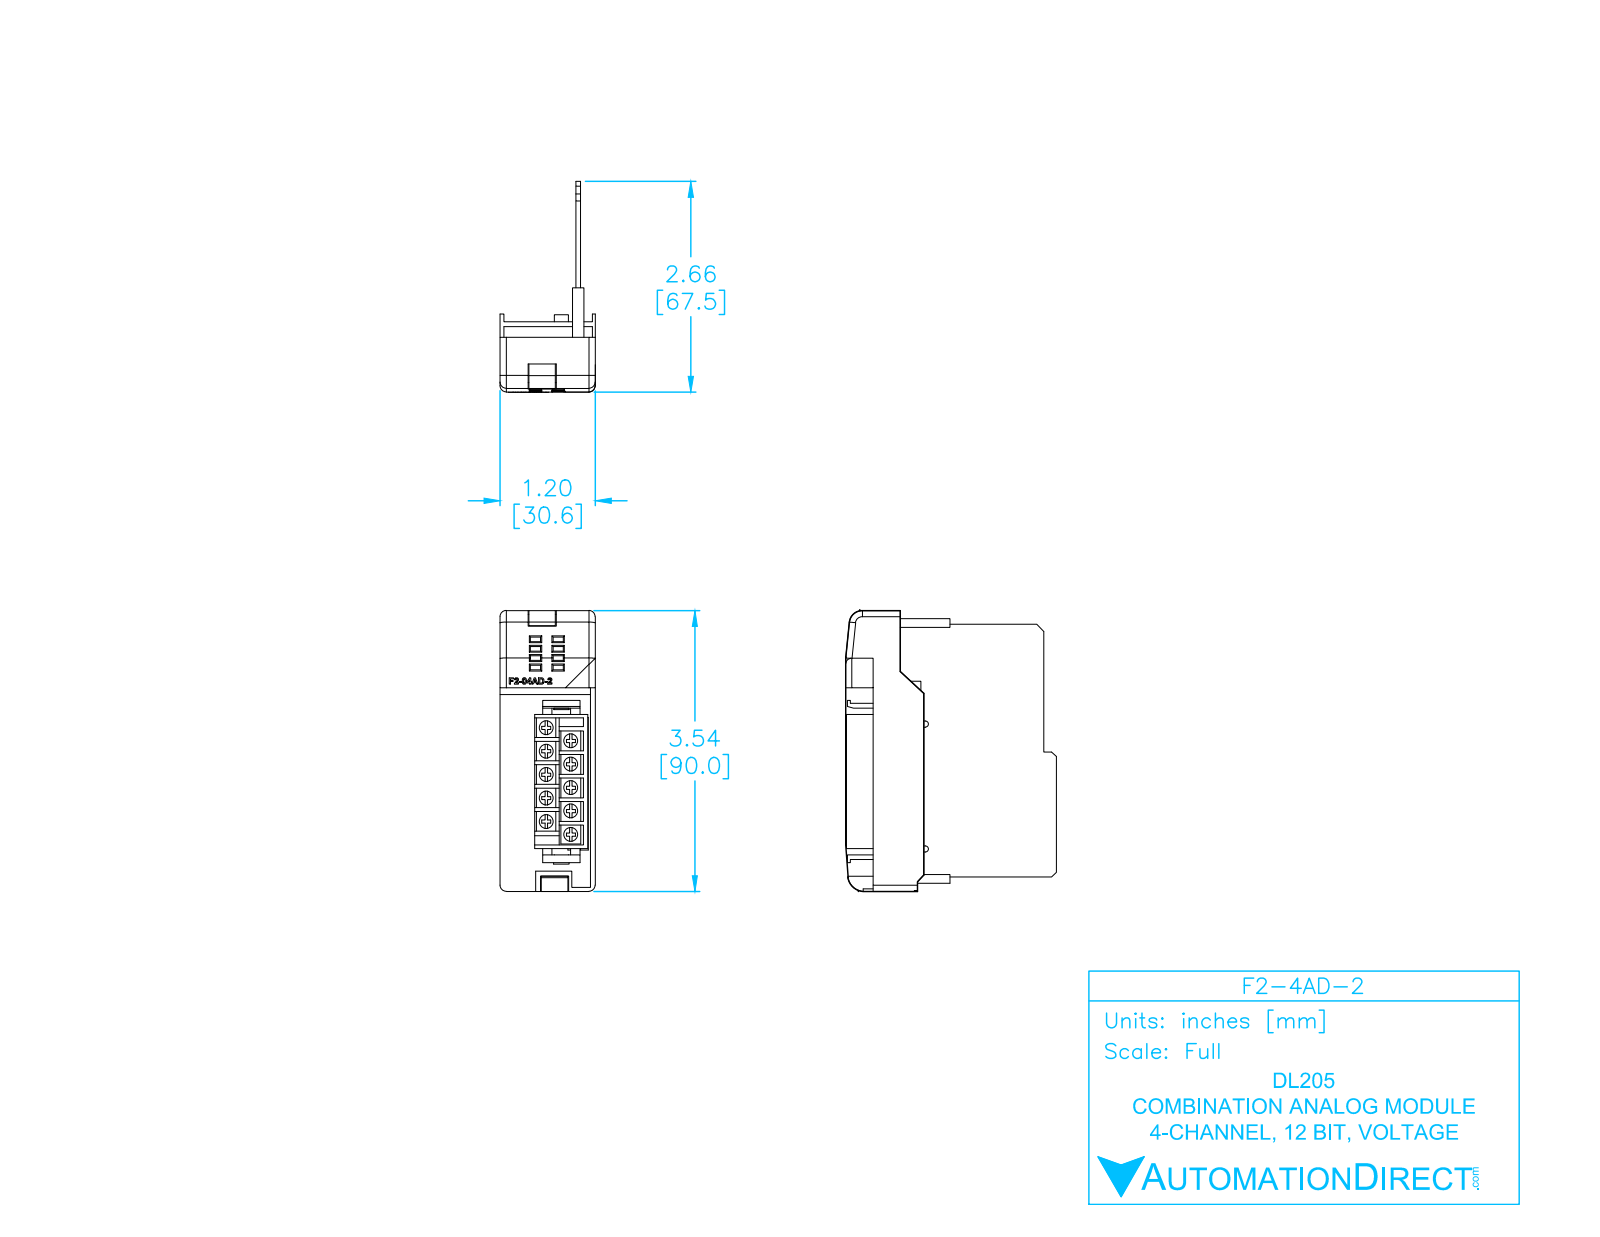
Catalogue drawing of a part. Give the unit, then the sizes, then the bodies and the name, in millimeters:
Units: millimetres
Overall size (bounding box): 90 × 67.61 × 30.55
Round bosses / shafts (diameter × count): ⌀4.5 ×10
Partial cylindrical surfaces — rounded edges, fillets, slot ends (radius × count): R0.35 ×16, R2 ×9, R0.25 ×2, R1 ×2, R1.25 ×2, R4.12 ×1, R5.39 ×1
Main face-to-face distances: 1.5, 4.72, 6.22, 2.37, 3.87, 2.35, 3.22, 0.85, 7.25, 8.14
Volume: 25 374 mm³ · Surface area: 28 533 mm²
Bodies: 6 solids, 582 faces (424 planar, 75 cylindrical, 83 other)
Part name (STEP PRODUCT): F2-04AD-2_ModuleCase_light_NEW
STEP written by: SolidWorks 2009 (AUTOMOTIVE_DESIGN)
